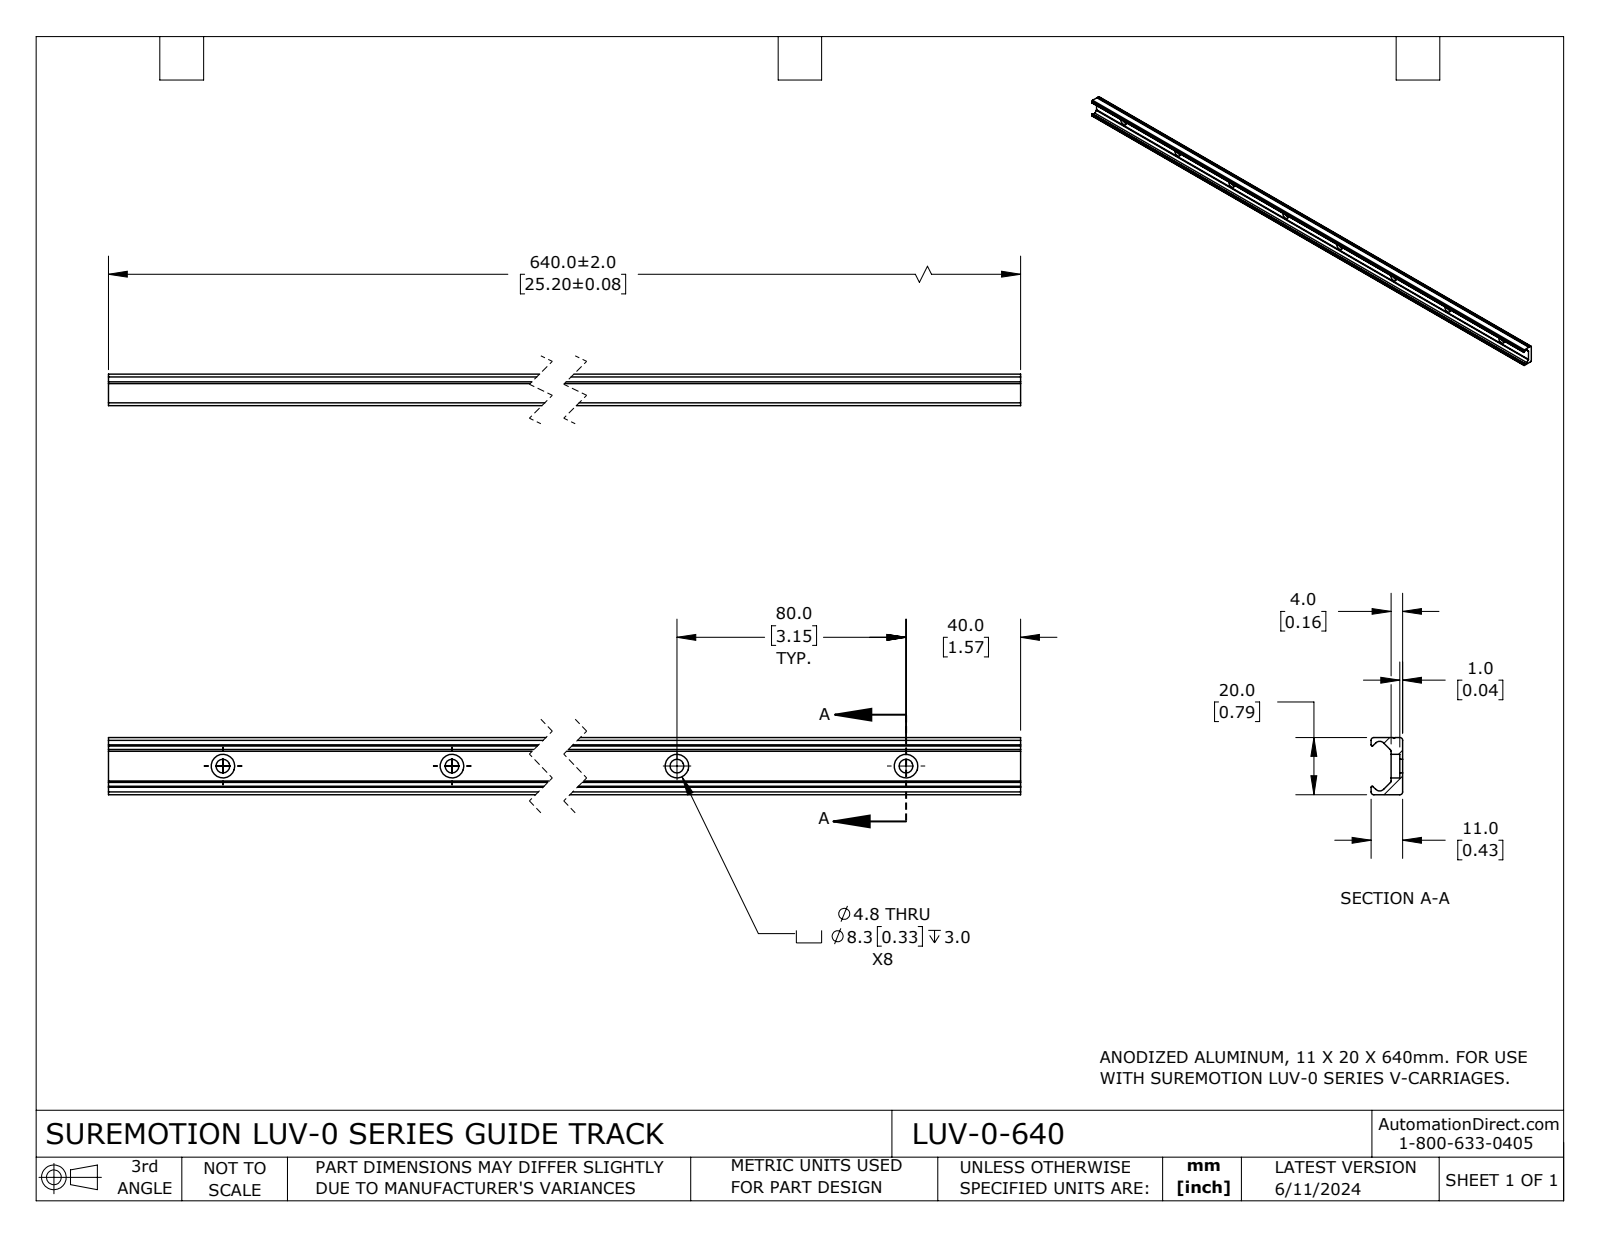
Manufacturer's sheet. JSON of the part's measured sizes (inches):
{"part_name": "LUV-0-640", "step_written_by": "SolidWorks 2023 (CONFIG_CONTROL_DESIGN)", "units": "inches", "bodies": {"solids": 1, "faces": 66, "planar": 21, "cylindrical": 45, "other": 0}, "overall_size": [25.197, 0.787, 0.433], "volume_in3": 4.31, "surface_area_in2": 75.24, "round_holes": [[0.189, 8], [0.325, 5], [0.325, 3]], "partial_cylinders_radius": [[0.039, 4], [0.015, 2], [0.016, 2], [0.031, 2], [0.078, 2], [0.013, 1]], "face_to_face_distances": [0.158, 0.787, 0.433, 0.275, 0.528, 0.04, 0.118, 0.393, 25.197], "hole_center_spacings": [3.15, 6.299, 9.449, 12.598, 15.748, 18.898, 22.047]}
